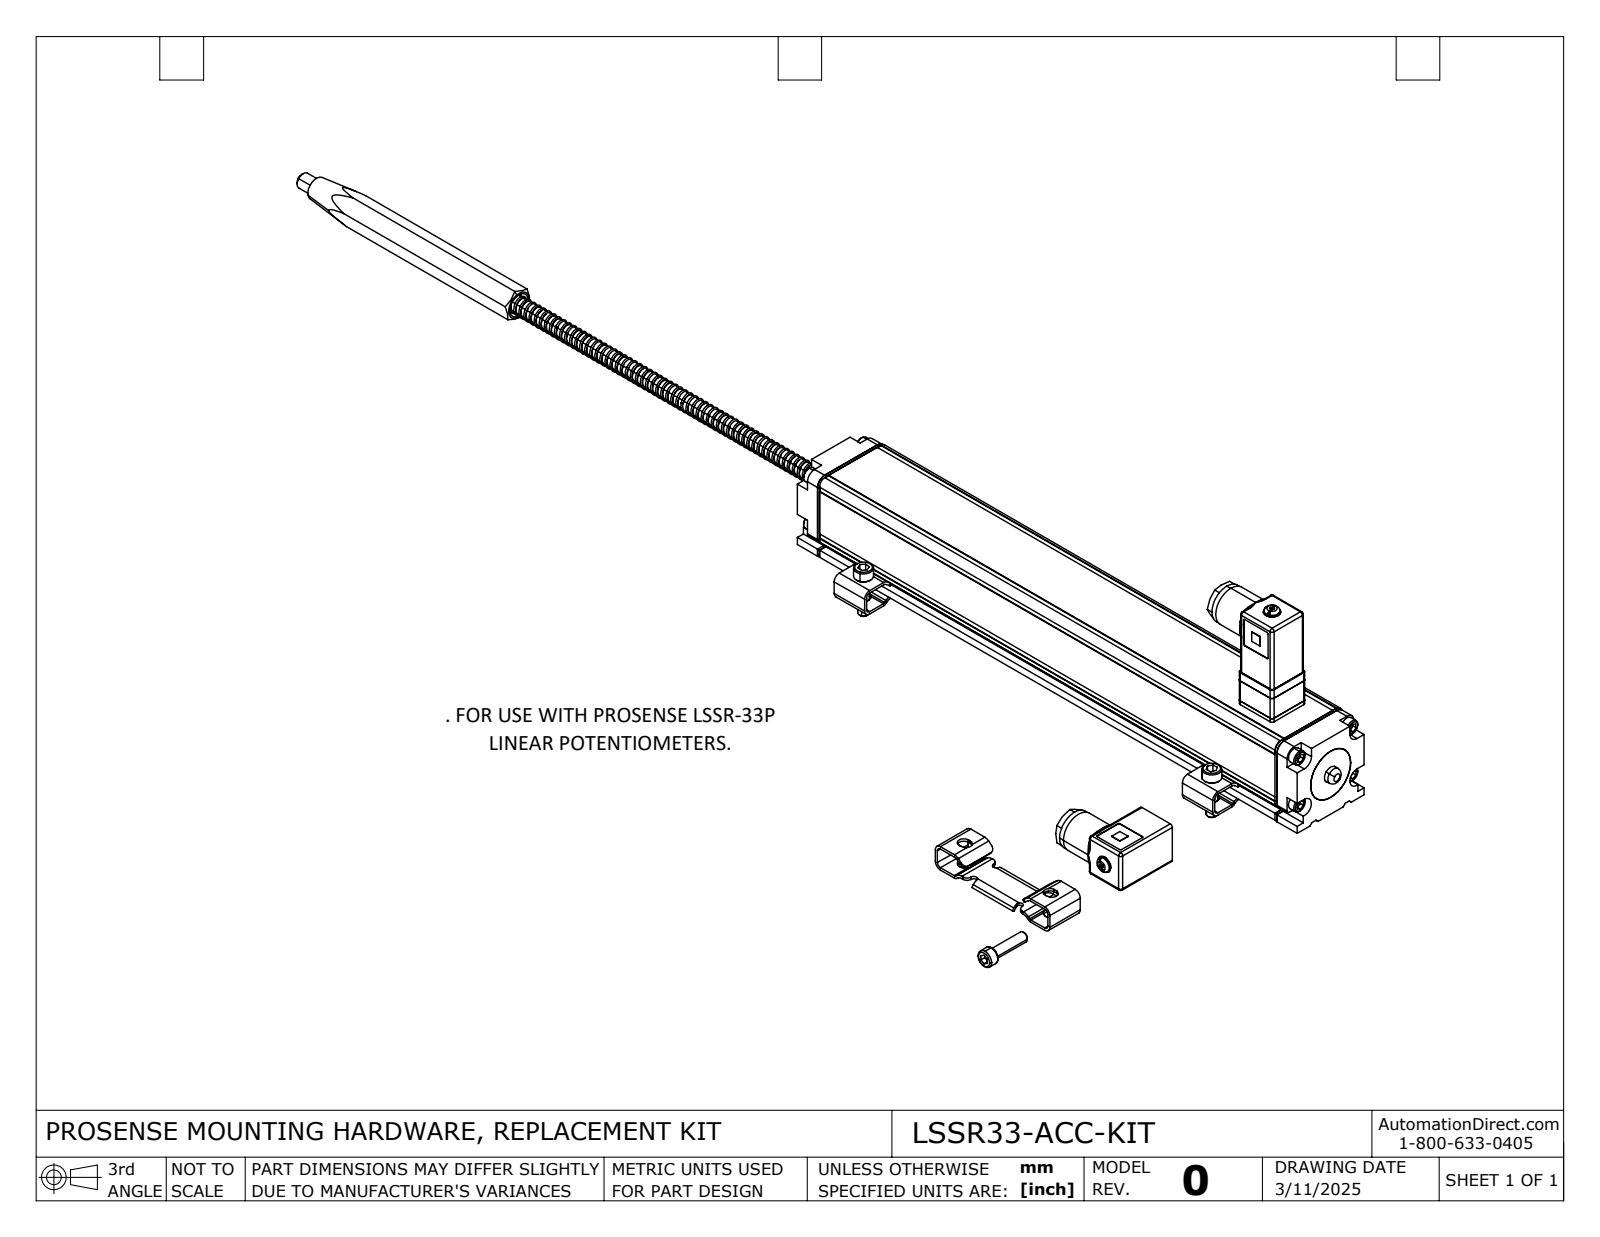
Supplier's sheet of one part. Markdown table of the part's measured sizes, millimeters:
| quantity | value |
| --- | --- |
| part name | LSSR33-ACC-KIT |
| STEP written by | SolidWorks 2024 (AUTOMOTIVE_DESIGN) |
| units | millimeters |
| bodies | 44 solids, 1872 faces (911 planar, 763 cylindrical, 198 other) |
| overall size | 512.55 × 176 × 82 |
| volume | 292 528 mm³ |
| surface area | 101 991 mm² |
| round holes (diameter × count) | 2.9 × 16, 3.5 × 8, 3.6 × 8, 1.4 × 4, 2.3 × 4, 5 × 4, 6.2 × 4, 18 × 4, 2 × 2, 2.75 × 2, 2.8 × 2, 3 × 2 |
| round bosses / shafts (diameter × count) | 2 × 16, 5.6 × 10, 3 × 8, 4 × 5, 7 × 4, 19.7 × 2, 15 × 2, 14.78 × 2 |
| partial cylindrical surfaces (radius × count) | 1 × 50, 2 × 32, 1.5 × 14, 3 × 14, 1.3 × 12, 2.25 × 12, 0.5 × 10, 2.5 × 8 |
| main face-to-face distances | 1, 32.8, 32.9, 3, 11, 226, 2, 10, 9, 0.8 |
| hole center spacings | 8.7, 13.88, 14.81, 19.97, 27, 5.19, 26.33, 27.1 |
